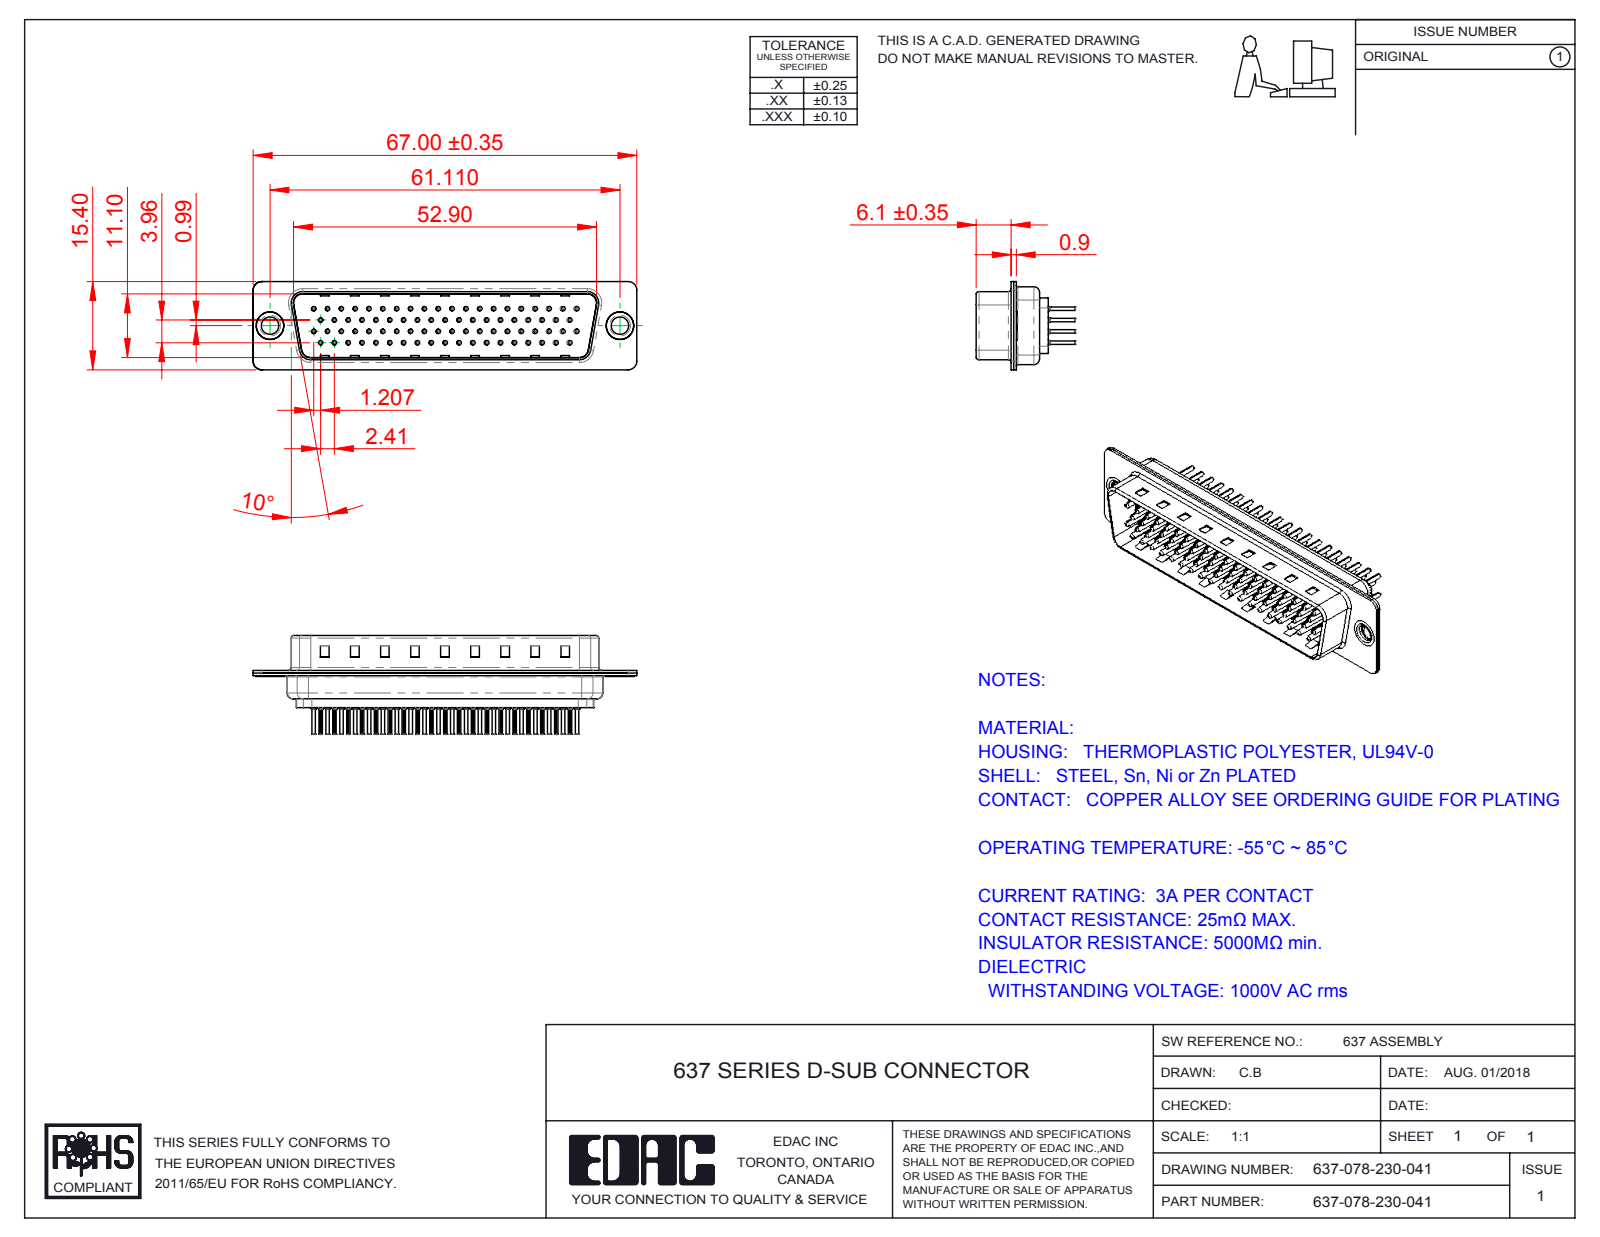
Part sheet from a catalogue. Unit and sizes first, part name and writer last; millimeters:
Units: millimetres
Overall size (bounding box): 67 × 17.25 × 15.4
Round holes (diameter × count): ⌀1.6 ×150, ⌀0.2 ×78, ⌀0.35 ×78, ⌀1.1 ×78, ⌀0.75 ×72, ⌀2 ×72, ⌀4 ×3, ⌀3.05 ×2, ⌀4.8 ×2
Round bosses / shafts (diameter × count): ⌀2 ×78, ⌀1.5 ×78, ⌀0.75 ×78, ⌀0.6 ×78, ⌀5 ×2, ⌀4.9 ×2, ⌀3.55 ×2, ⌀4.8 ×1
Partial cylindrical surfaces — rounded edges, fillets, slot ends (radius × count): R0.1 ×156, R1.5 ×16, R2 ×12, R0.5 ×8, R0.25 ×4, R0.55 ×4, R0.7 ×4, R0.95 ×4
Main face-to-face distances: 0.45, 0.4, 1.5, 1.95, 11.9, 11.5, 0.7, 11.1, 0.9, 0.8
Hole centre spacings: 2.41, 7.24, 6.06, 9.65, 6.96, 8.46, 14.54, 16.89
Volume: 4 257 mm³ · Surface area: 15 718 mm²
Bodies: 83 solids, 8186 faces (2075 planar, 3011 cylindrical, 3100 other)
Part name (STEP PRODUCT): 637 Shell Front_78 Contacts; 637 Thru Hole Rivet; 637 Contact Row 1_30; 637 Shell Rear_78 Contacts (+5 more)
STEP written by: SolidWorks 2016 (CONFIG_CONTROL_DESIGN)
